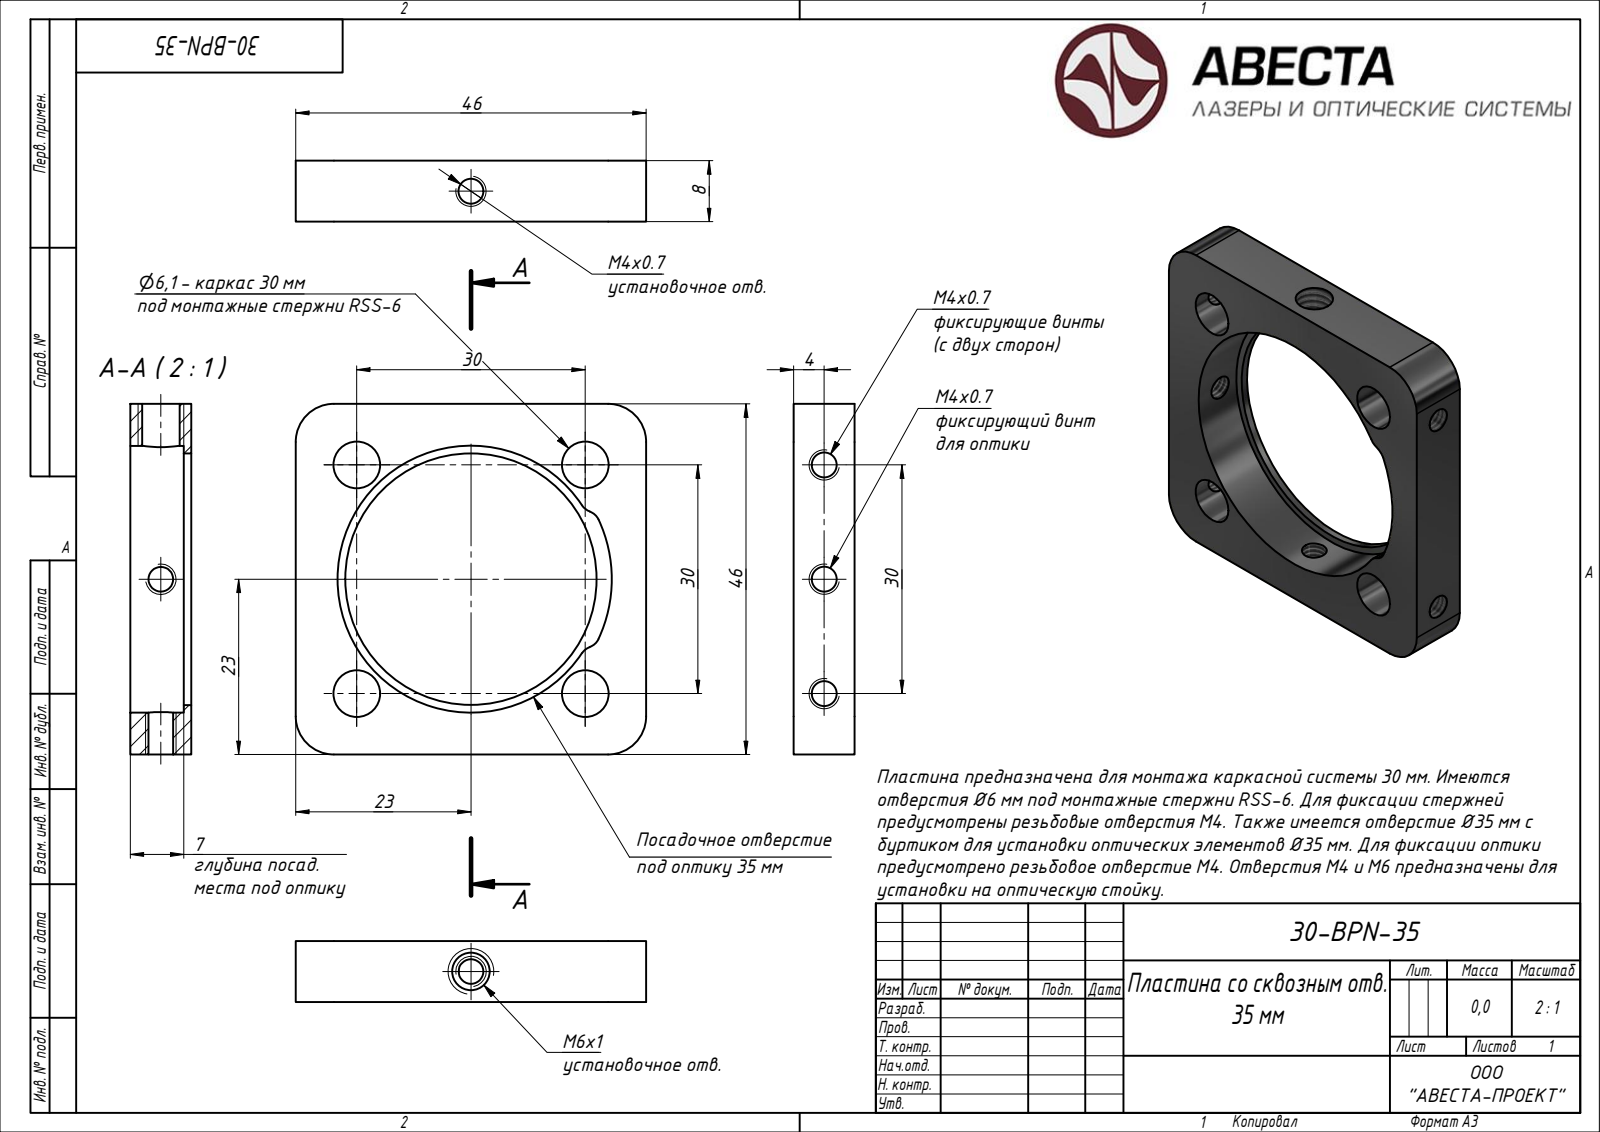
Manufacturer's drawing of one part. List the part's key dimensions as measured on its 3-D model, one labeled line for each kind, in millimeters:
Part name (STEP PRODUCT): 30-BPN-35
STEP written by: Autodesk Inventor 2020 (AUTOMOTIVE_DESIGN)
Units: millimetres
Bodies: 1 solid, 29 faces (7 planar, 22 cylindrical, 0 other)
Overall size (bounding box): 46 × 46 × 8
Volume: 7 738 mm³ · Surface area: 5 417 mm²
Round holes (diameter × count): ⌀3.24 ×4, ⌀6.1 ×4, ⌀4.92 ×1, ⌀33 ×1, ⌀35 ×1
Partial cylindrical surfaces — rounded edges, fillets, slot ends (radius × count): R2 ×4, R5 ×4, R18.5 ×1
Main face-to-face distances: 8, 46, 7, 1
Hole centre spacings: 30, 21.21, 15, 42.43
